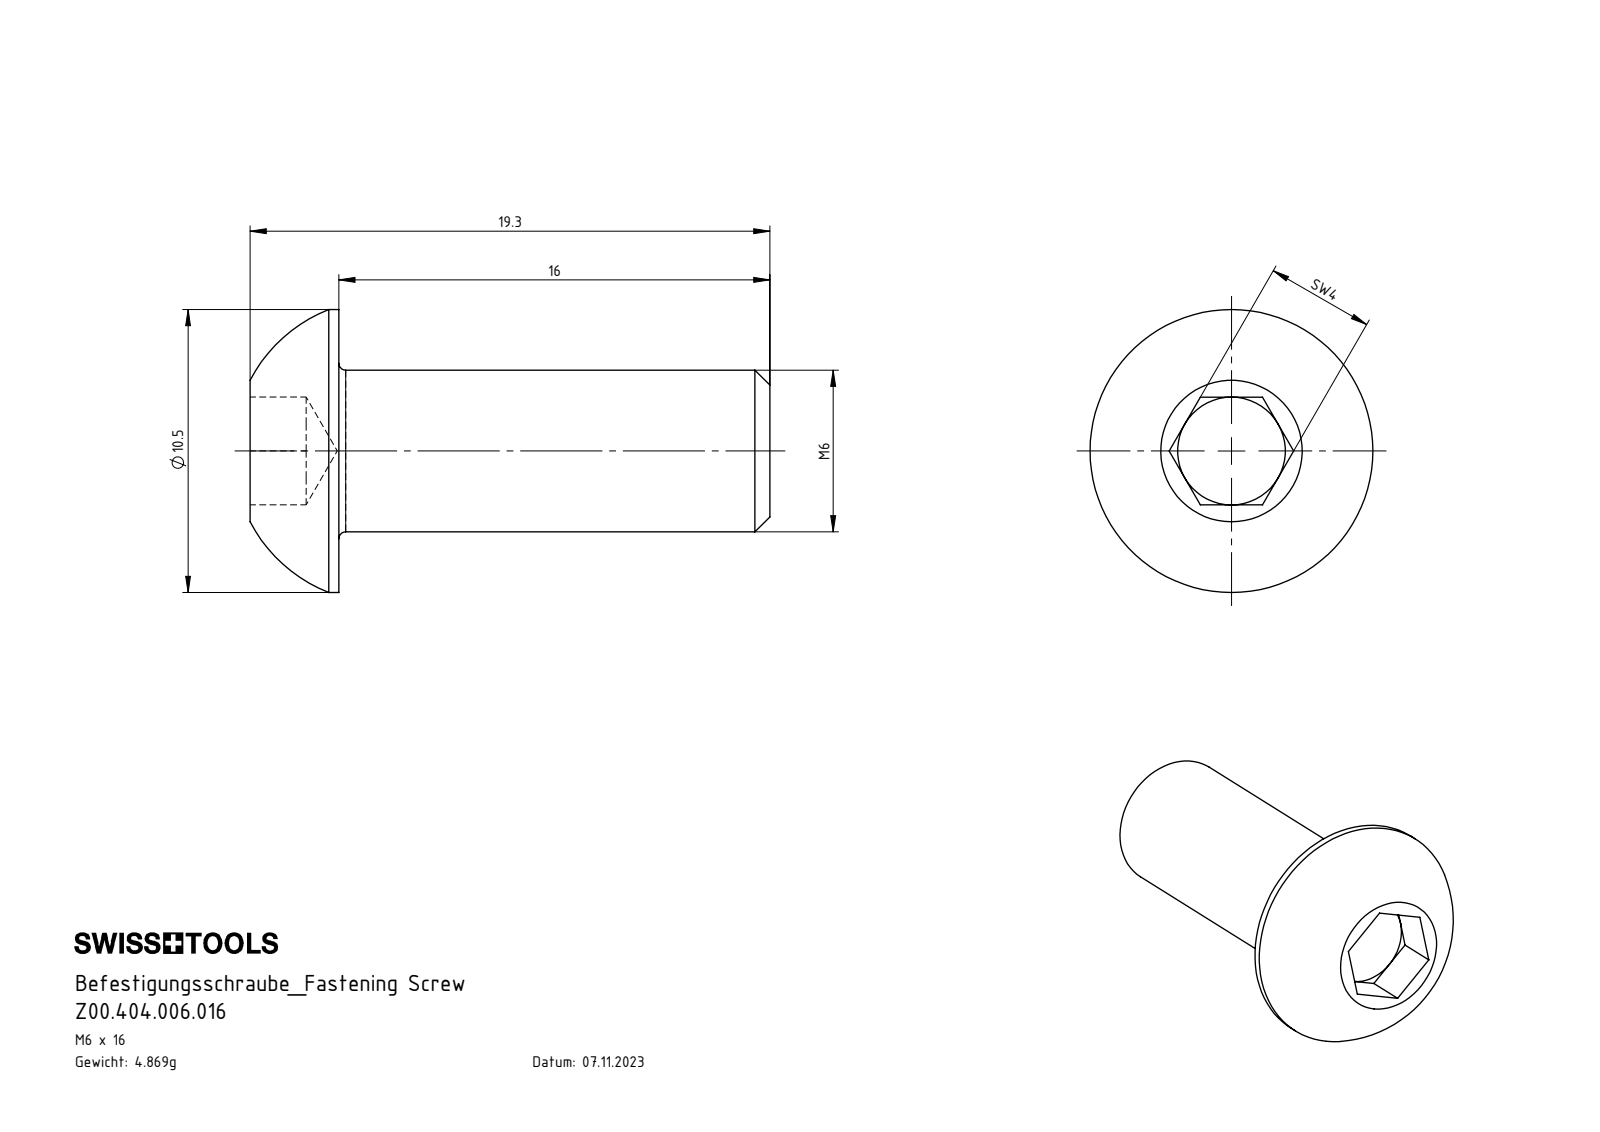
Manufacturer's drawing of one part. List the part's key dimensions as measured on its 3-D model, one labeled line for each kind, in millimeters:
Part name (STEP PRODUCT): Z00.404.006.016
STEP written by: SolidWorks 2022 (AUTOMOTIVE_DESIGN)
Units: millimetres
Bodies: 1 solid, 27 faces (15 planar, 4 cylindrical, 8 other)
Overall size (bounding box): 19.3 × 10.5 × 10.5
Volume: 620 mm³ · Surface area: 548 mm²
Round bosses / shafts (diameter × count): ⌀10.5 ×1, ⌀6 ×1
Main face-to-face distances: 16, 4, 3.3, 19.3, 2.08, 1.22, 17.22
